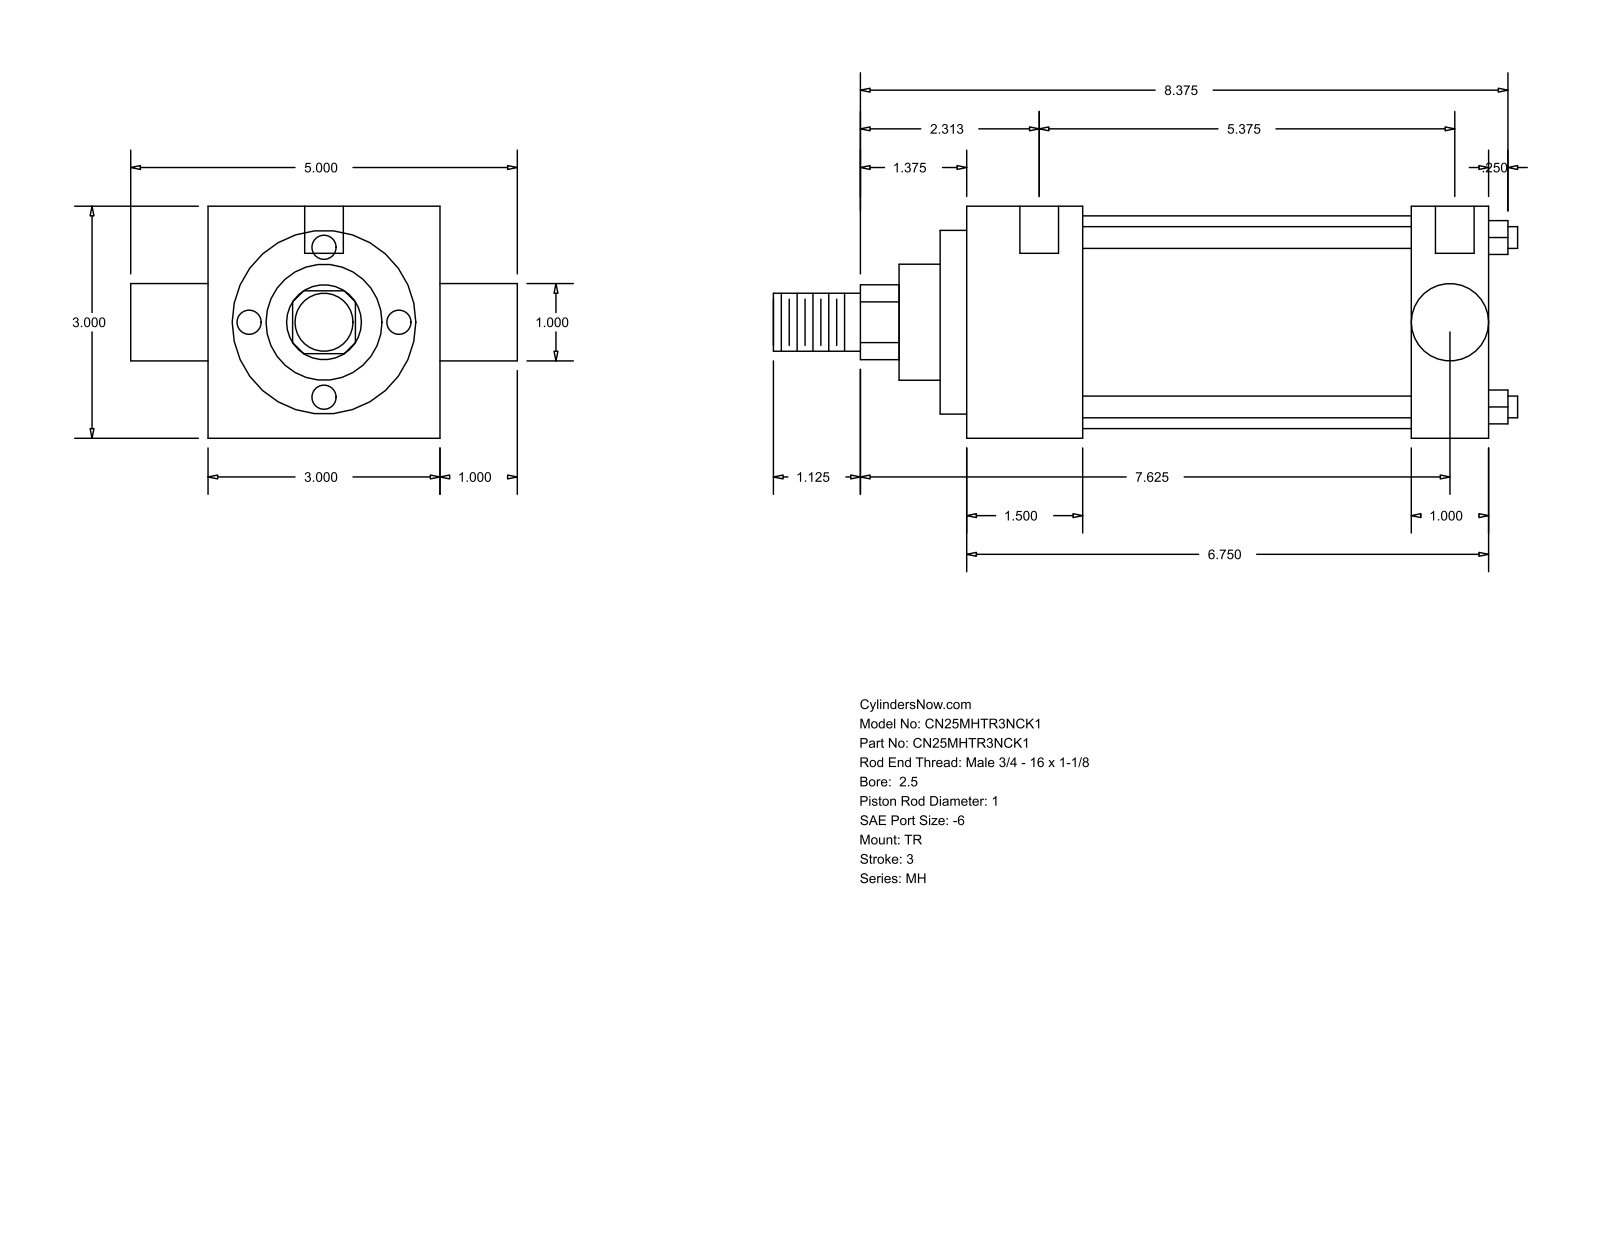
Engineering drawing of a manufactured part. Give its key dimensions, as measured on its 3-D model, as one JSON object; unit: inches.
{"part_name": "MH_TR__0250_1", "step_written_by": "GSSL Pune (CONFIG_CONTROL_DESIGN)", "units": "inches", "bodies": {"solids": 0, "faces": 86, "planar": 61, "cylindrical": 25, "other": 0}, "overall_size": [9.625, 5, 3], "round_holes": [[0.219, 3], [0.5, 2]], "round_bosses_or_shafts": [[0.281, 4], [2.75, 1], [2.375, 1], [1.5, 1], [1, 1], [0.998, 1], [0.75, 1]], "partial_cylinders_radius": [[0.484, 1]], "face_to_face_distances": [3, 6.75, 1.5, 5.25, 5.75, 4.25, 1, 0.344, 1.844, 6.094], "hole_center_spacings": [0.125, 0.187, 5.375, 5.5, 5.562, 5.687]}
